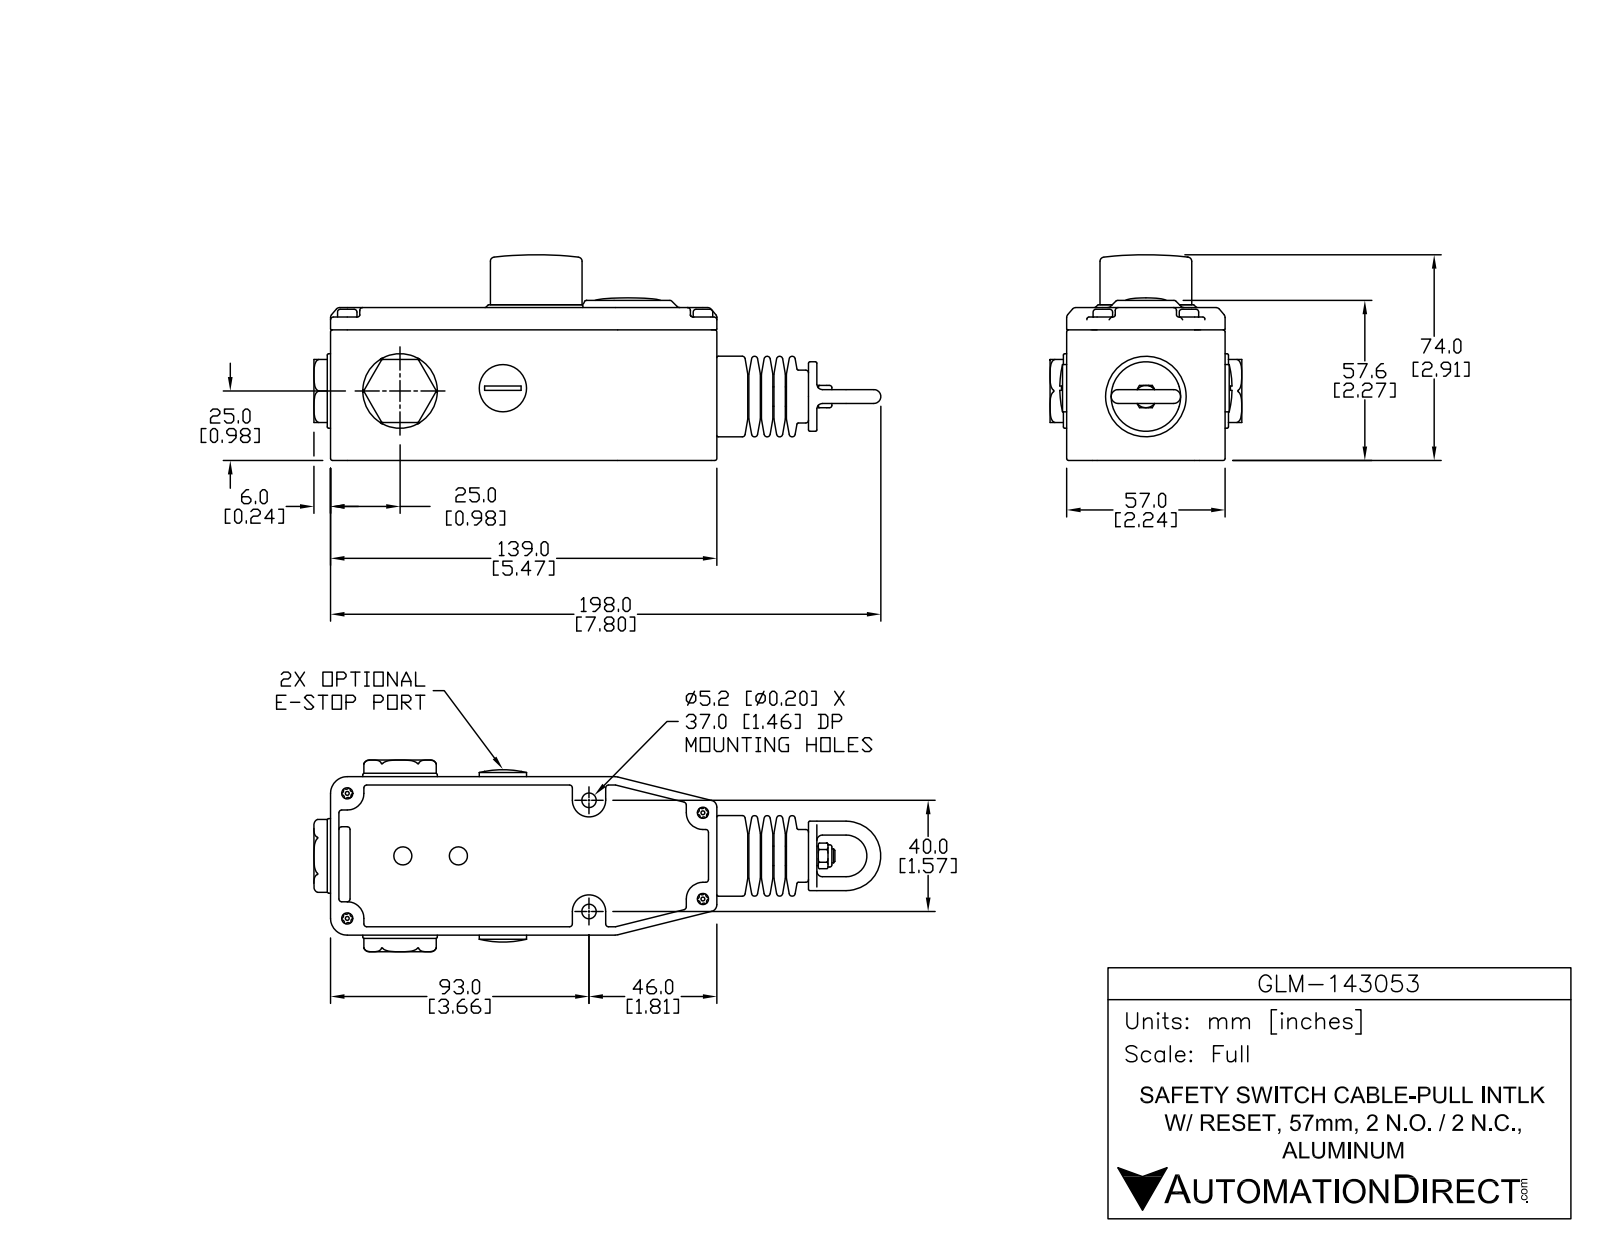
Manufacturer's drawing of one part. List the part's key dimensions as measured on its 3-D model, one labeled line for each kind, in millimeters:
Part name (STEP PRODUCT): GLM-143053
STEP written by: SolidWorks 2013 (AUTOMOTIVE_DESIGN)
Units: millimetres
Bodies: 1 solid, 424 faces (127 planar, 146 cylindrical, 151 other)
Overall size (bounding box): 204 × 73.9 × 69.8
Volume: 455 129 mm³ · Surface area: 49 813 mm²
Round holes (diameter × count): ⌀4 ×4, ⌀5.2 ×2
Round bosses / shafts (diameter × count): ⌀7 ×5, ⌀26.8 ×2, ⌀5 ×2, ⌀35.2 ×1, ⌀33 ×1, ⌀29 ×1, ⌀25 ×1, ⌀19 ×1
Partial cylindrical surfaces — rounded edges, fillets, slot ends (radius × count): R0.5 ×30, R0.16 ×19, R0.25 ×12, R1 ×8, R4.5 ×2, R4.57 ×2, R7 ×2, R13 ×2
Main face-to-face distances: 54.68, 57.2, 55, 0.32, 139, 6.3, 63.5, 18.9, 73.58, 73.9
Hole centre spacings: 31, 40, 41.24, 41.25, 45, 54.21, 54.25, 87.03
